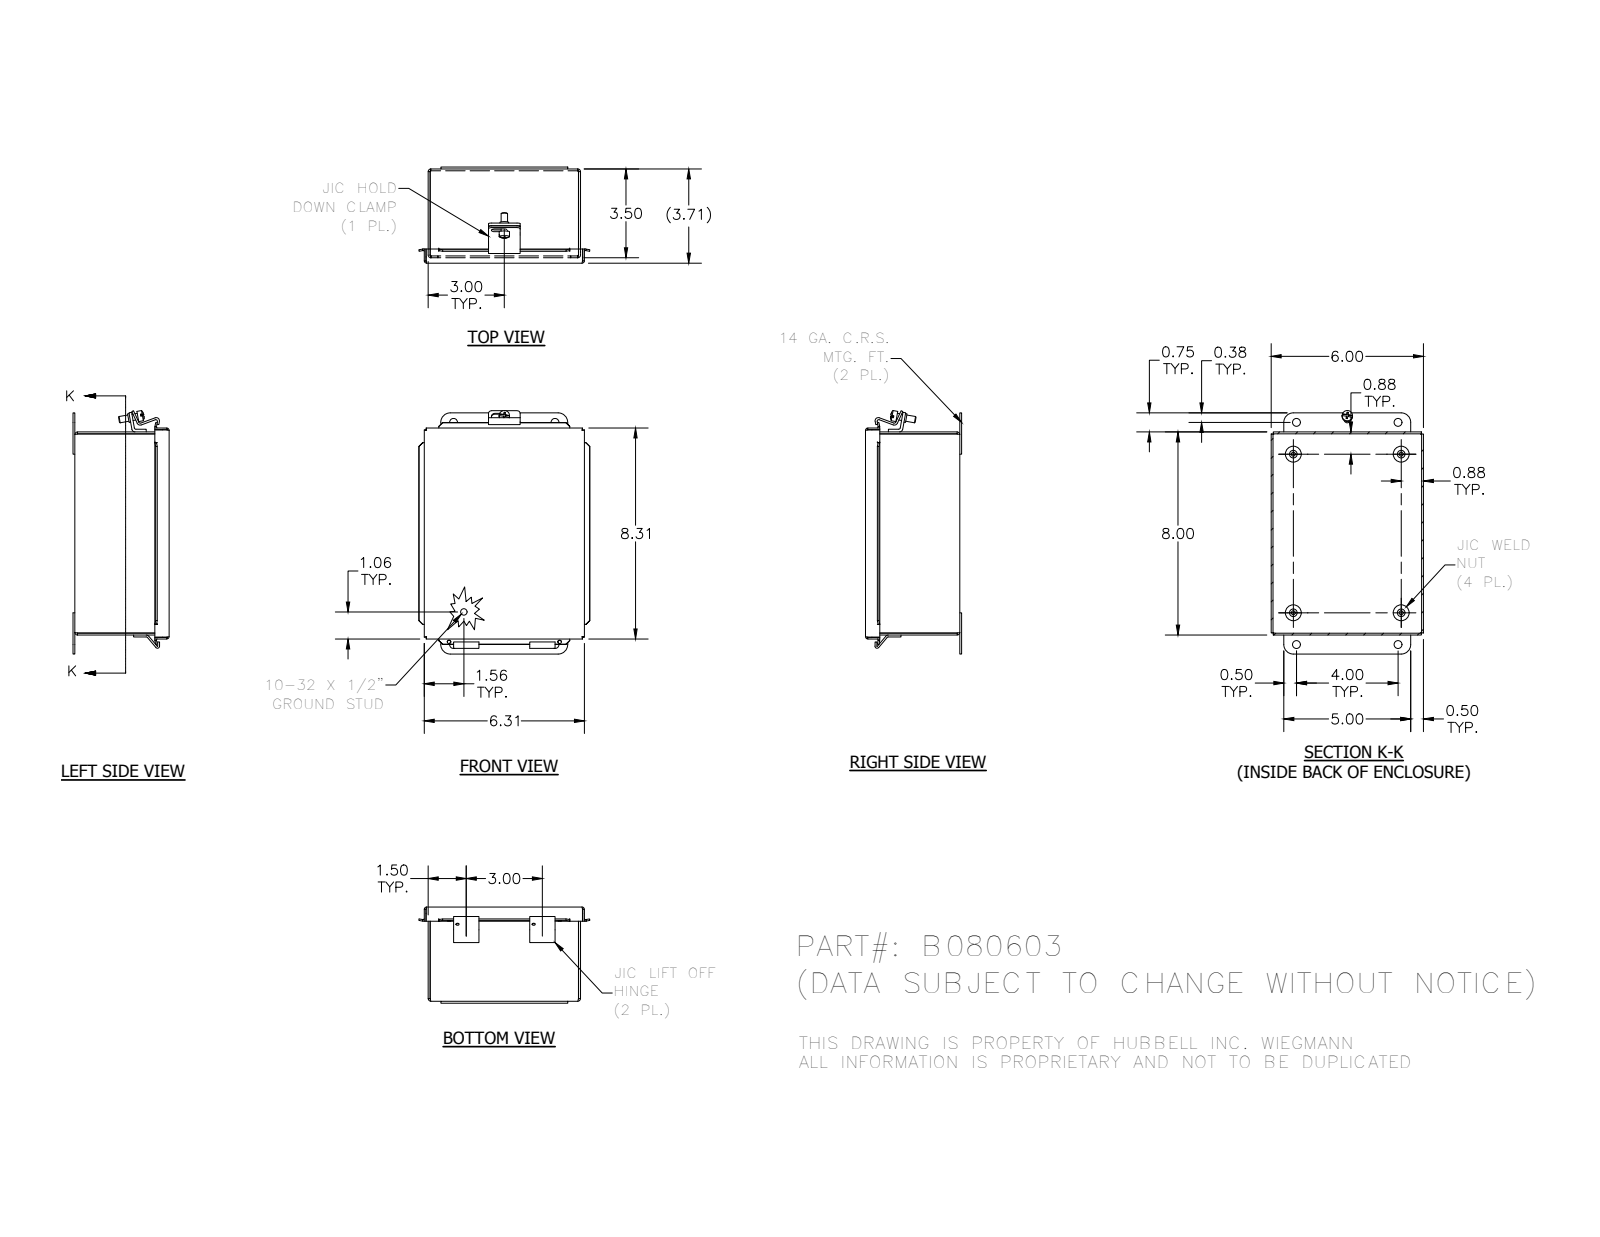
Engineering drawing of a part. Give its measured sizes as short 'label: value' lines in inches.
name: B080603; 3499; 3482; C1001 (+7 more)
written by: Autodesk Inventor 2012 (AUTOMOTIVE_DESIGN)
unit: in
bodies: 16 solids, 369 faces (245 planar, 82 cylindrical, 42 other)
size: 9.593 × 6.739 × 3.787
volume: 20.37 in³; area: 541.4 in²
holes: 4× ⌀0.156, 4× ⌀0.31, 2× ⌀0.125, 2× ⌀0.14, 1× ⌀0.196
bosses: 4× ⌀0.625, 4× ⌀0.3, 2× ⌀0.25, 1× ⌀0.41, 1× ⌀0.344, 1× ⌀0.19
rounds: 16× R0.031, 8× R0.093, 8× R0.105, 4× R0.125, 4× R0.375, 3× R0.063, 3× R0.126, 2× R0.133
face distances: 0.074, 3.65, 5.926, 3.712, 0.062, 3.576, 3.638, 7.926, 6, 5.852
hole spacings: 1.257, 7.501, 8.559, 4, 4.25, 4.31, 4.311, 6.25
